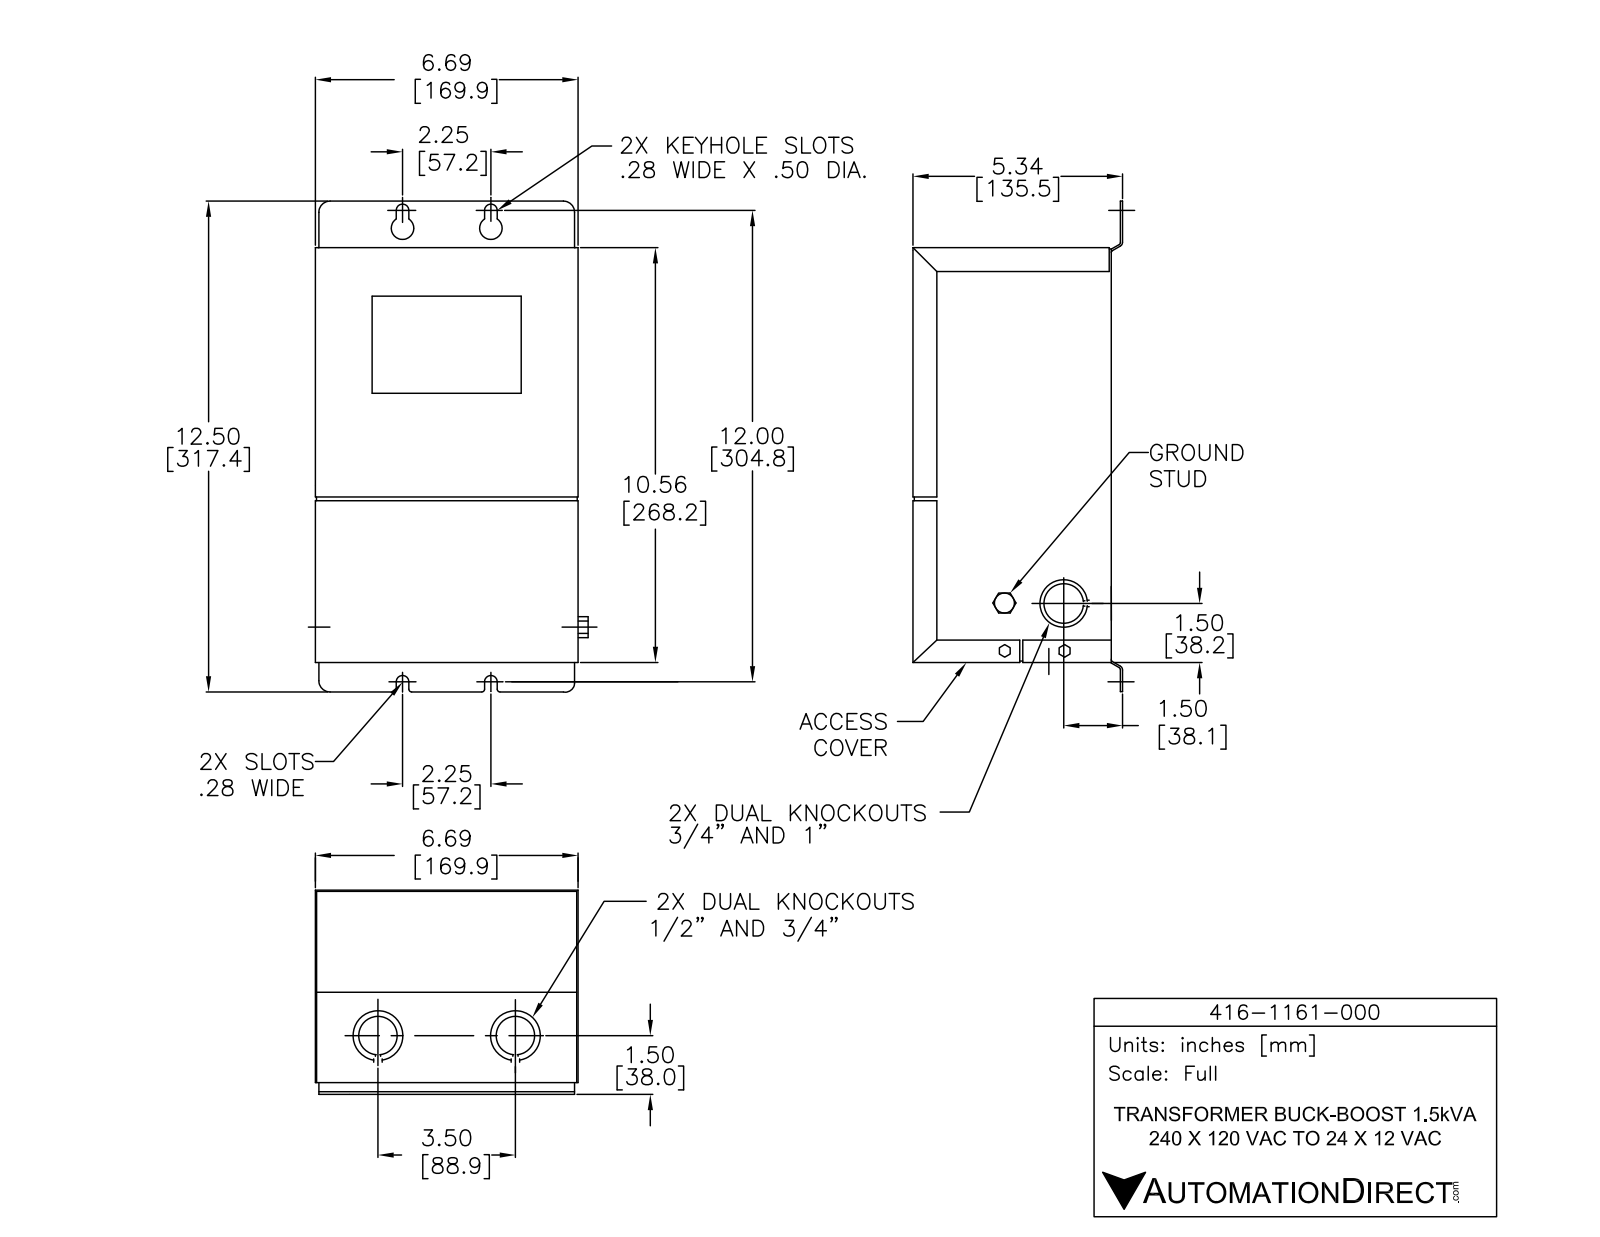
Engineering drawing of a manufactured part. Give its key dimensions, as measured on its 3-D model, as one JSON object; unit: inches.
{"part_name": "416-1161-000", "step_written_by": "SolidWorks 2013 (AUTOMOTIVE_DESIGN)", "units": "inches", "bodies": {"solids": 1, "faces": 186, "planar": 114, "cylindrical": 64, "other": 8}, "overall_size": [12.5, 6.9, 5.341], "volume_in3": 362.1, "surface_area_in2": 348.2, "round_holes": [[0.5, 2], [0.875, 2], [0.24, 1], [0.29, 1], [0.875, 1]], "round_bosses_or_shafts": [[1.11, 2], [1.125, 1]], "partial_cylinders_radius": [[0.04, 10], [0.25, 10], [0.14, 5], [0.08, 2], [0.1, 1], [0.167, 1], [0.207, 1]], "face_to_face_distances": [5.12, 6.62, 0.04, 10.64, 6.66, 5.121, 6.7, 5.3, 0.18, 5.301], "hole_center_spacings": [1.361, 1.371, 2.25, 2.35, 3.5]}
